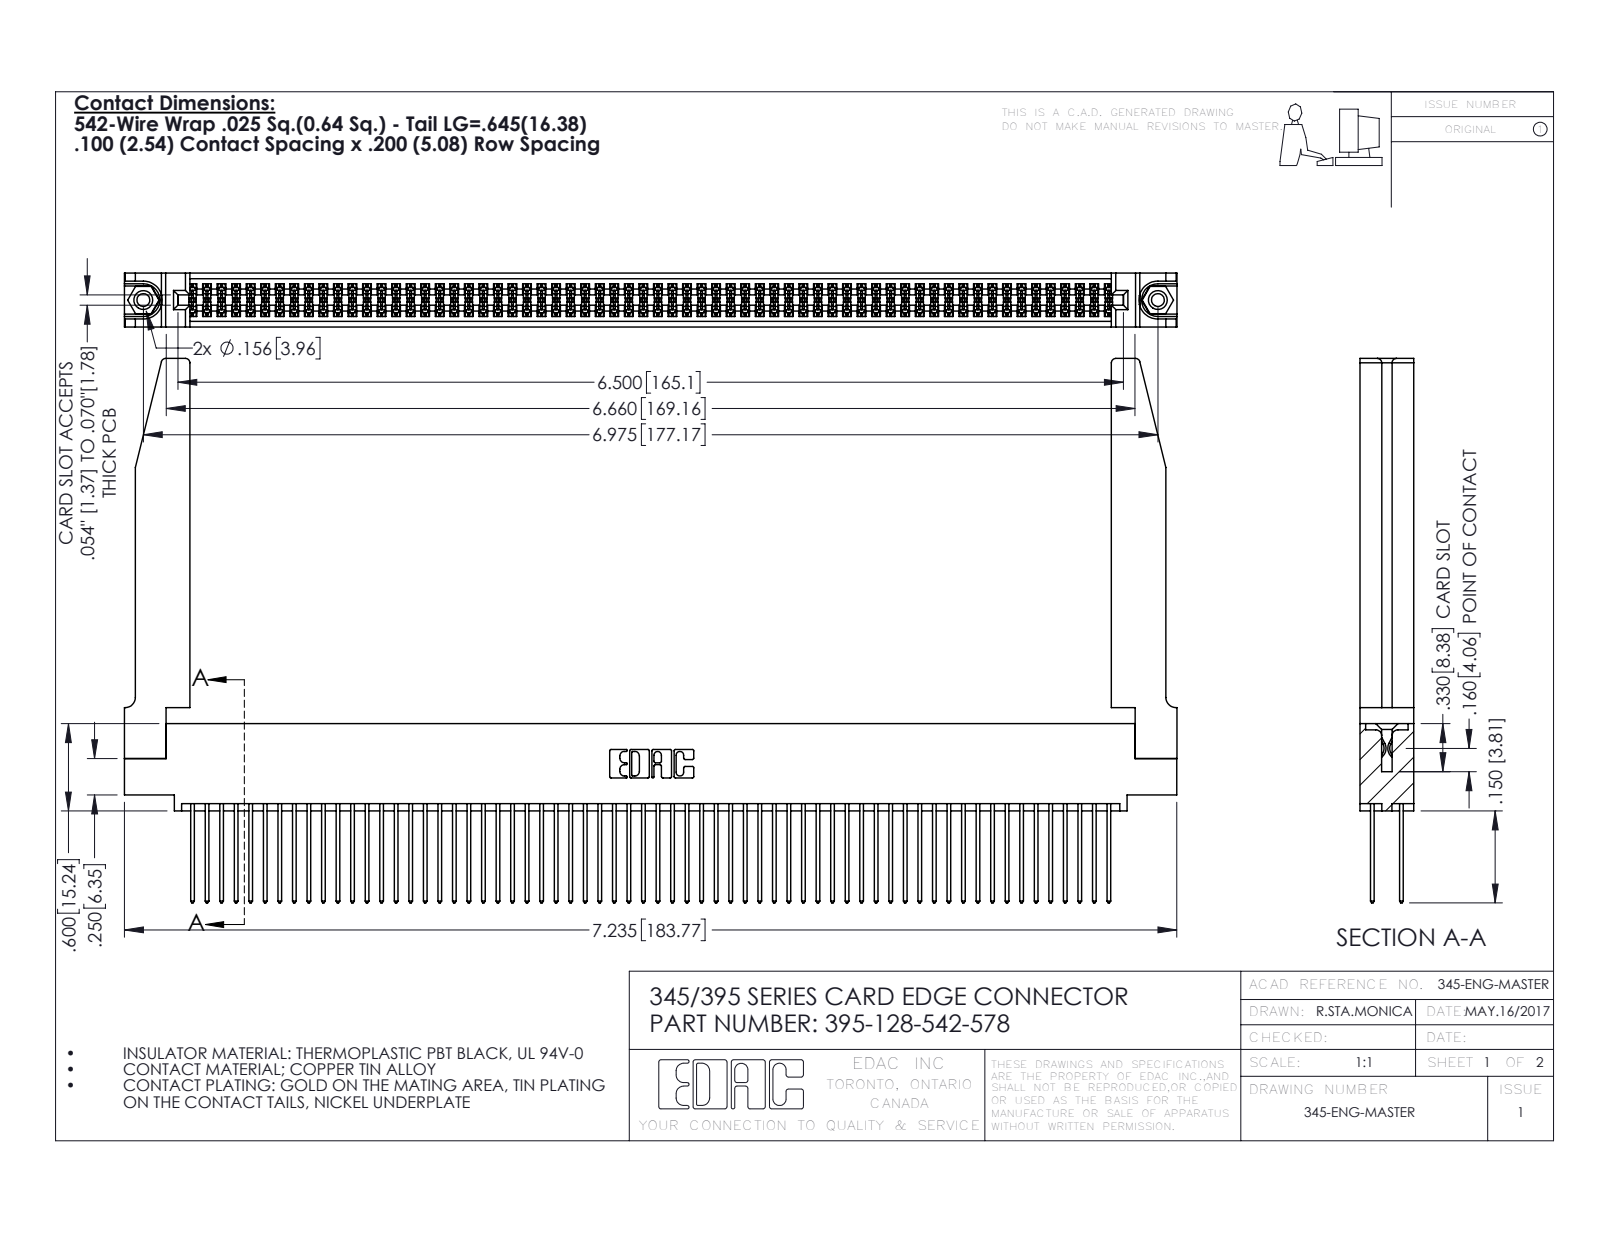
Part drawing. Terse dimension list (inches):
name: 395-128-542-578; 345-220-078_345-220-078; 345 Part_0.110 Offset - 0.156 Dia-TH; 345-250-001_345-250-001-102 (+1 more)
written by: SolidWorks 2016 (CONFIG_CONTROL_DESIGN)
unit: in
bodies: 133 solids, 6764 faces (4450 planar, 2262 cylindrical, 52 other)
size: 7.236 × 3.742 × 0.37
volume: 1.608 in³; area: 58.3 in²
holes: 2× ⌀0.089, 2× ⌀0.125, 2× ⌀0.156, 1× ⌀0.064
bosses: 2× ⌀0.155
rounds: 192× R0.006, 128× R0.01, 22× R0.01, 8× R0.03, 6× R0.007, 6× R0.031, 3× R0.026, 2× R0.014
face distances: 0.072, 0.298, 0.37, 0.098, 0.272, 0.025, 0.2, 0.225, 0.175, 0.148
hole spacings: 0.27, 6.739, 6.975
